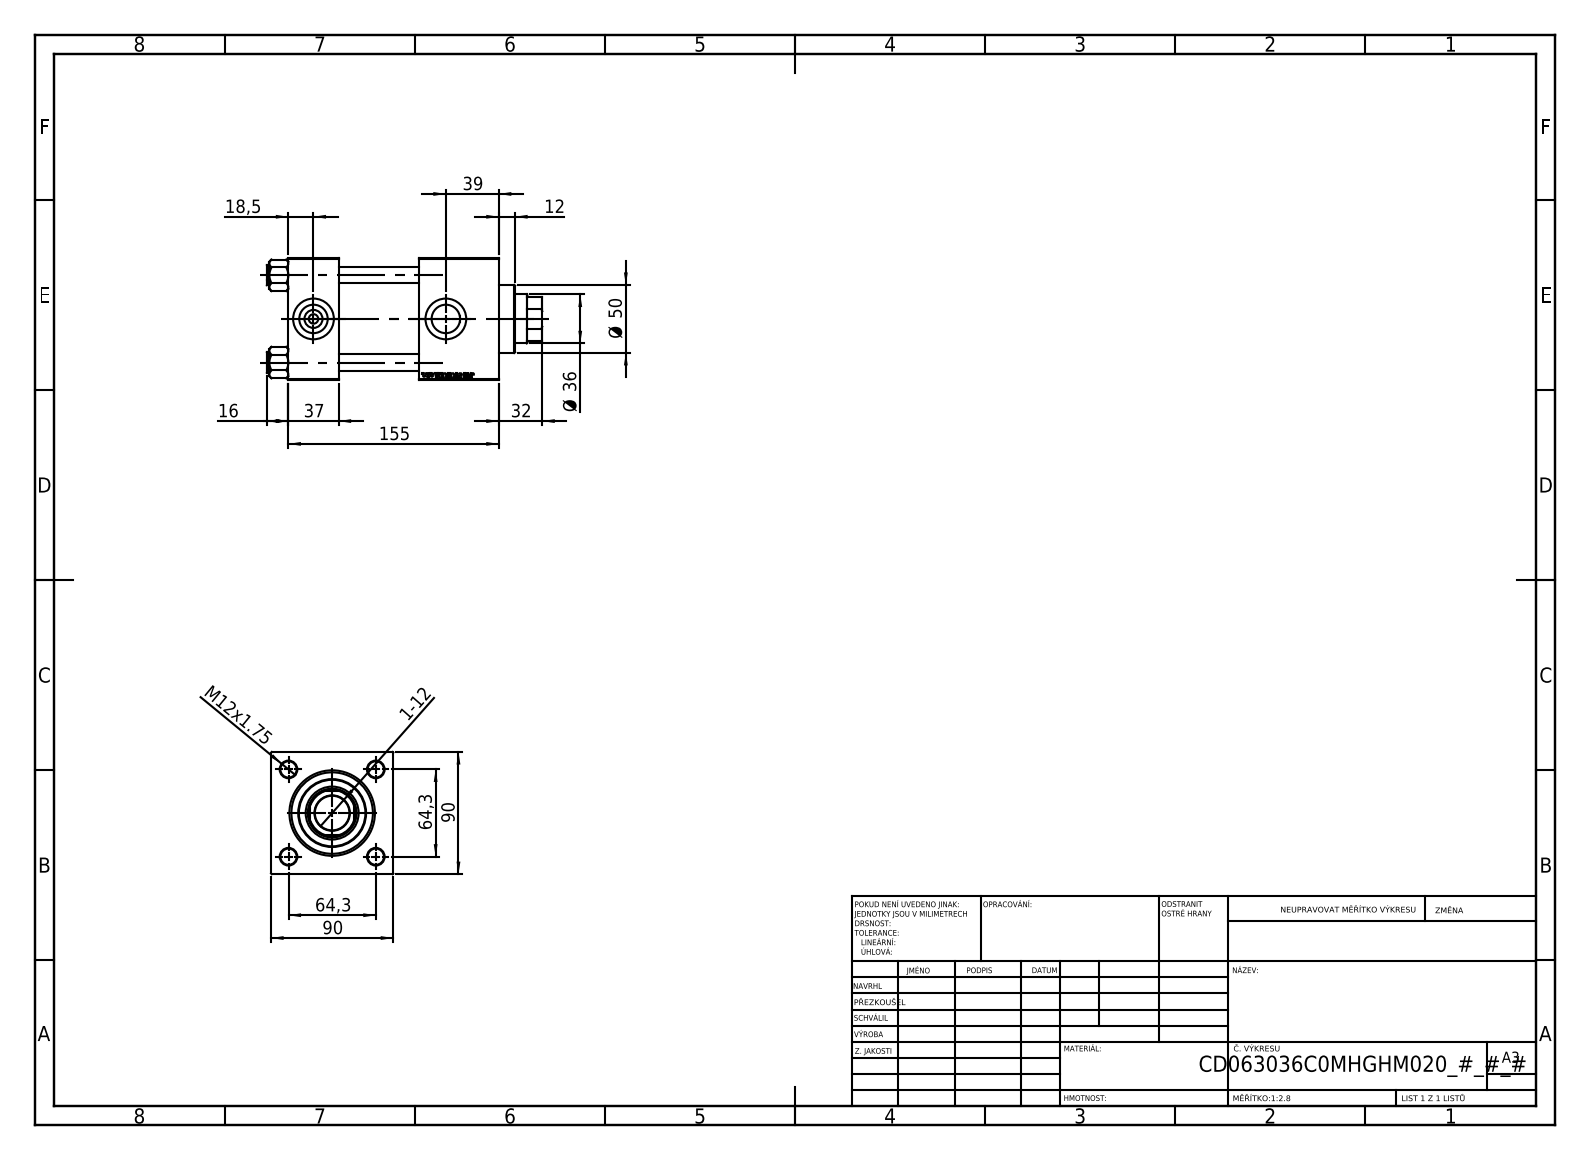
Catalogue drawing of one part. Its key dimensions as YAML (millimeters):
part_name: "V215CD_Body_C; V215CD_C_TYCINKA; NUT_M5_V215CD_C; V215CD_VC_C (+1 more)"
step_written_by: "SolidWorks 2019 (CONFIG_CONTROL_DESIGN)"
units: millimeters
bodies: {solids: 11, faces: 1148, planar: 526, cylindrical: 86, other: 536}
overall_size: [203, 90, 90]
volume: 967956
surface_area: 184233
round_holes:
  - {diameter: 12, count: 4}
  - {diameter: 7, count: 2}
  - {diameter: 20.96, count: 2}
  - {diameter: 30, count: 2}
  - {diameter: 25.5, count: 1}
  - {diameter: 36, count: 1}
  - {diameter: 39, count: 1}
  - {diameter: 50, count: 1}
  - {diameter: 60, count: 1}
  - {diameter: 63, count: 1}
round_bosses_or_shafts:
  - {diameter: 15, count: 4}
  - {diameter: 69, count: 1}
partial_cylinders:
  - {radius: 17.5, count: 1}
face_to_face_distances: [90, 59, 37, 155, 118, 96, 126.3, 89.3, 30.3, 28.7]
hole_center_spacings: [45.47, 64.3, 90.93, 97.5]
